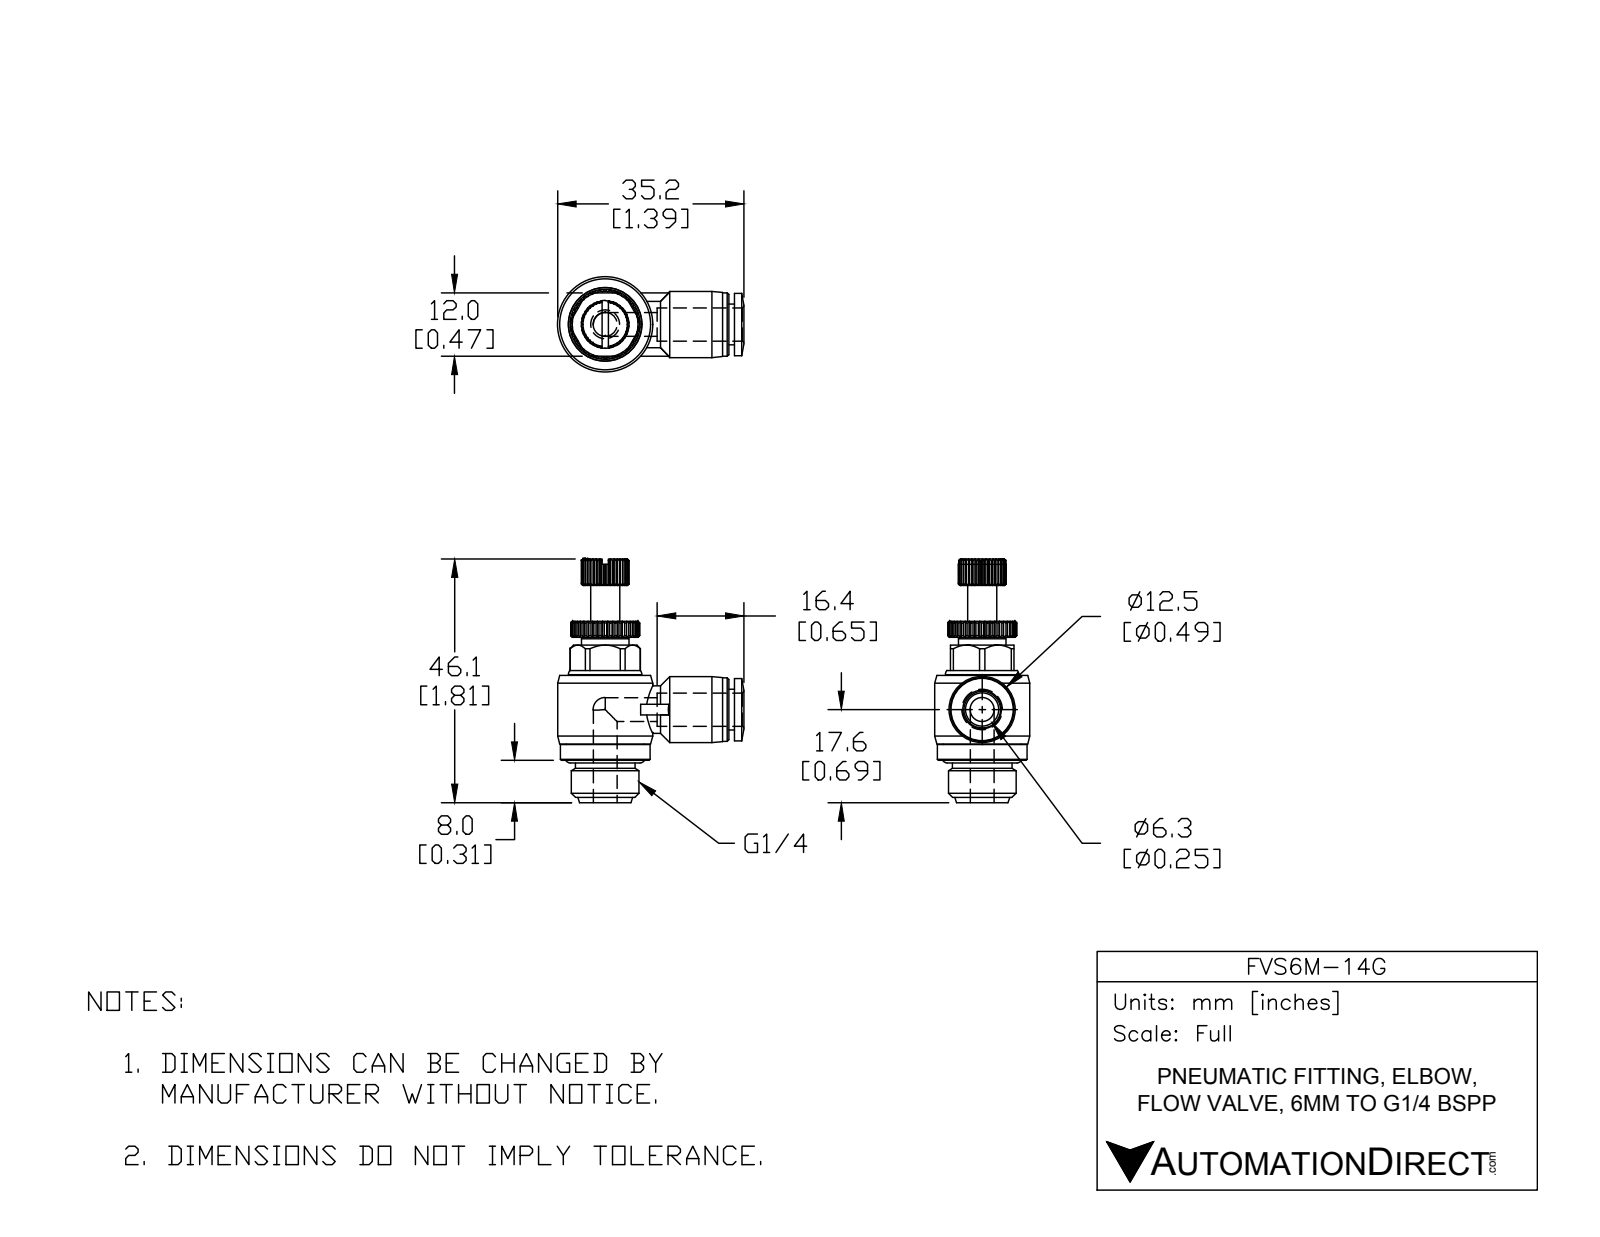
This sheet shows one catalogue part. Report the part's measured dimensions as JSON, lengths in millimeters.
{"part_name": "FVS6M-14G", "step_written_by": "SolidWorks 2015 (AUTOMOTIVE_DESIGN)", "units": "millimeters", "bodies": {"solids": 2, "faces": 516, "planar": 196, "cylindrical": 118, "other": 202}, "overall_size": [46.1, 35.3, 18], "volume_mm3": 7490, "surface_area_mm2": 4566, "round_holes": [[4.5, 2], [6.3, 1]], "round_bosses_or_shafts": [[9, 2], [18, 1], [17, 1], [14.8, 1], [13.4, 1], [12.8, 1], [12.5, 1], [12, 1]], "partial_cylinders_radius": [[6.5, 1], [6.7, 1]], "face_to_face_distances": [10.2, 12, 3, 7.2, 5.9, 23.3, 23.2, 13.1, 13, 20.2]}
